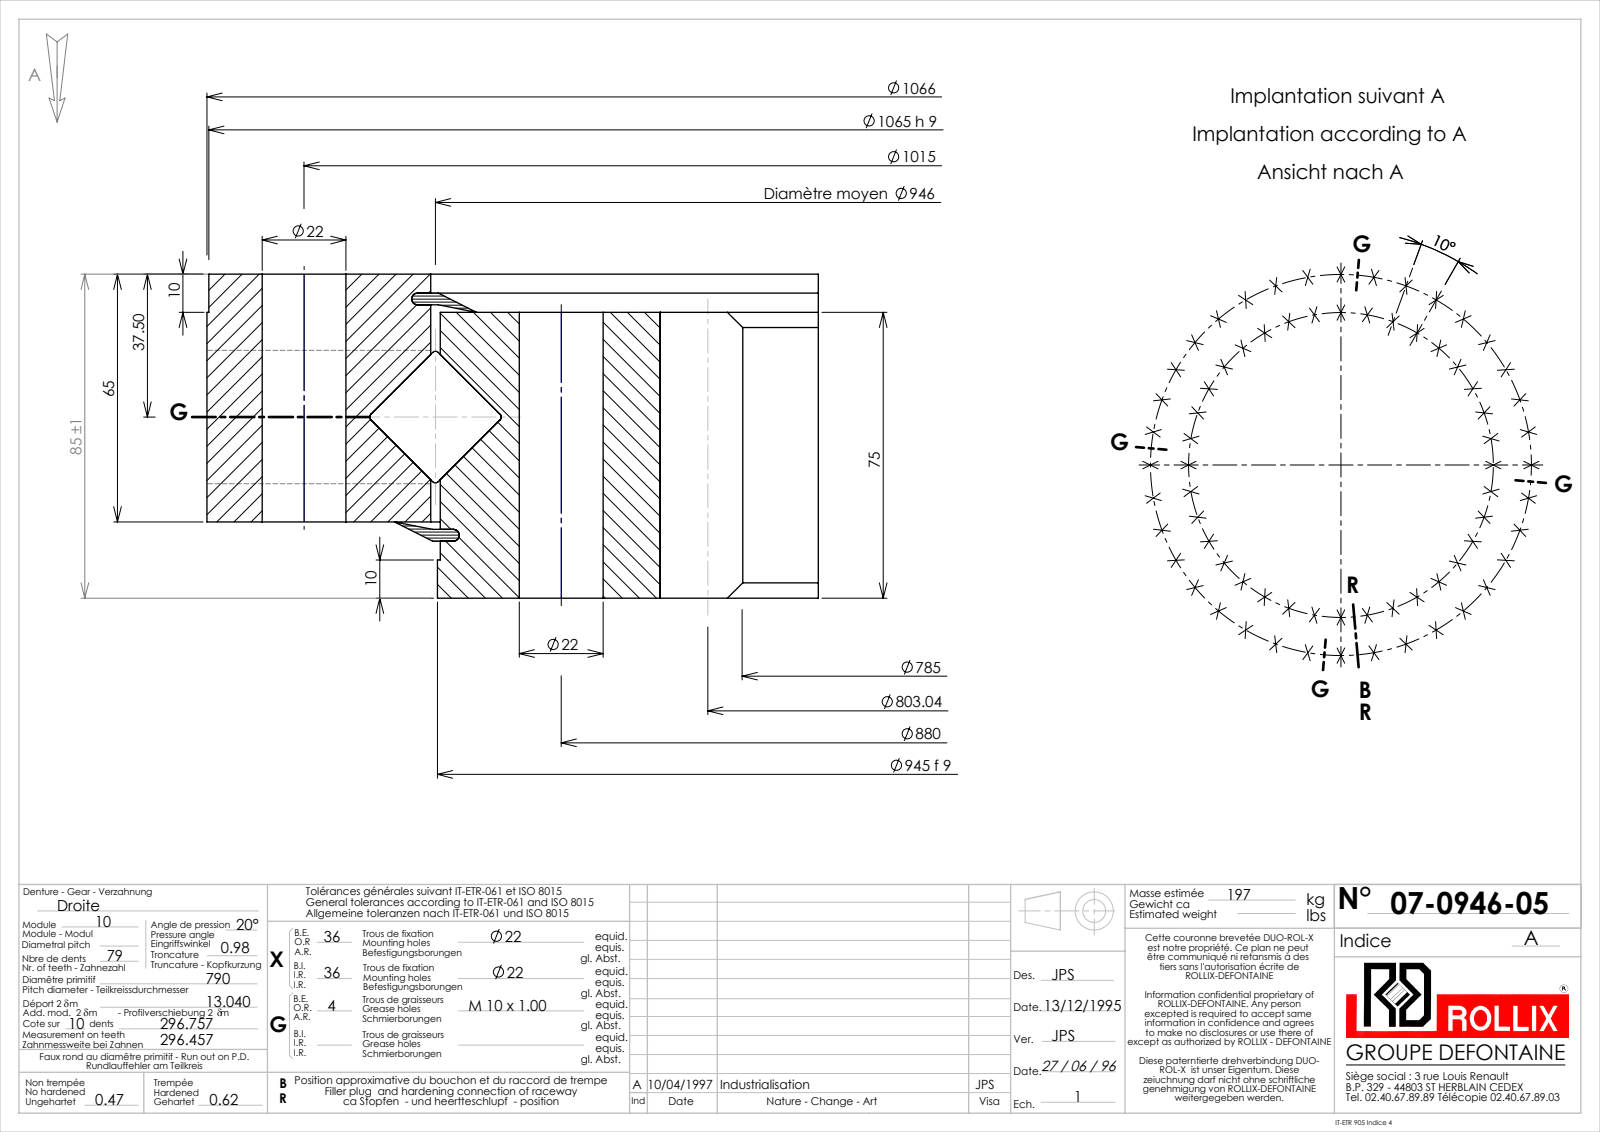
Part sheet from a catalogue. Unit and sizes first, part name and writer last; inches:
Units: inches
Overall size (bounding box): 41.969 × 41.969 × 3.346
Round holes (diameter × count): ⌀0.866 ×72, ⌀0.354 ×4, ⌀37.343 ×1
Round bosses / shafts (diameter × count): ⌀41.969 ×1, ⌀41.929 ×1, ⌀37.205 ×1, ⌀37.146 ×1, ⌀0.984 ×1
Partial cylindrical surfaces — rounded edges, fillets, slot ends (radius × count): R15.453 ×1, R16.3 ×1
Main face-to-face distances: 2.953, 0.394, 2.559, 0.787, 2.165, 3.346, 0.199, 2.364, 0.077, 2.242
Hole centre spacings: 6.016, 22.27, 8.967, 14.642, 3.02, 19.872, 33.465, 34.514
Volume: 1 400 in³ · Surface area: 3 722 in²
Bodies: 5 solids, 705 faces (174 planar, 331 cylindrical, 200 other)
Part name (STEP PRODUCT): 07-0946-05
STEP written by: SolidWorks 2016 (CONFIG_CONTROL_DESIGN)
